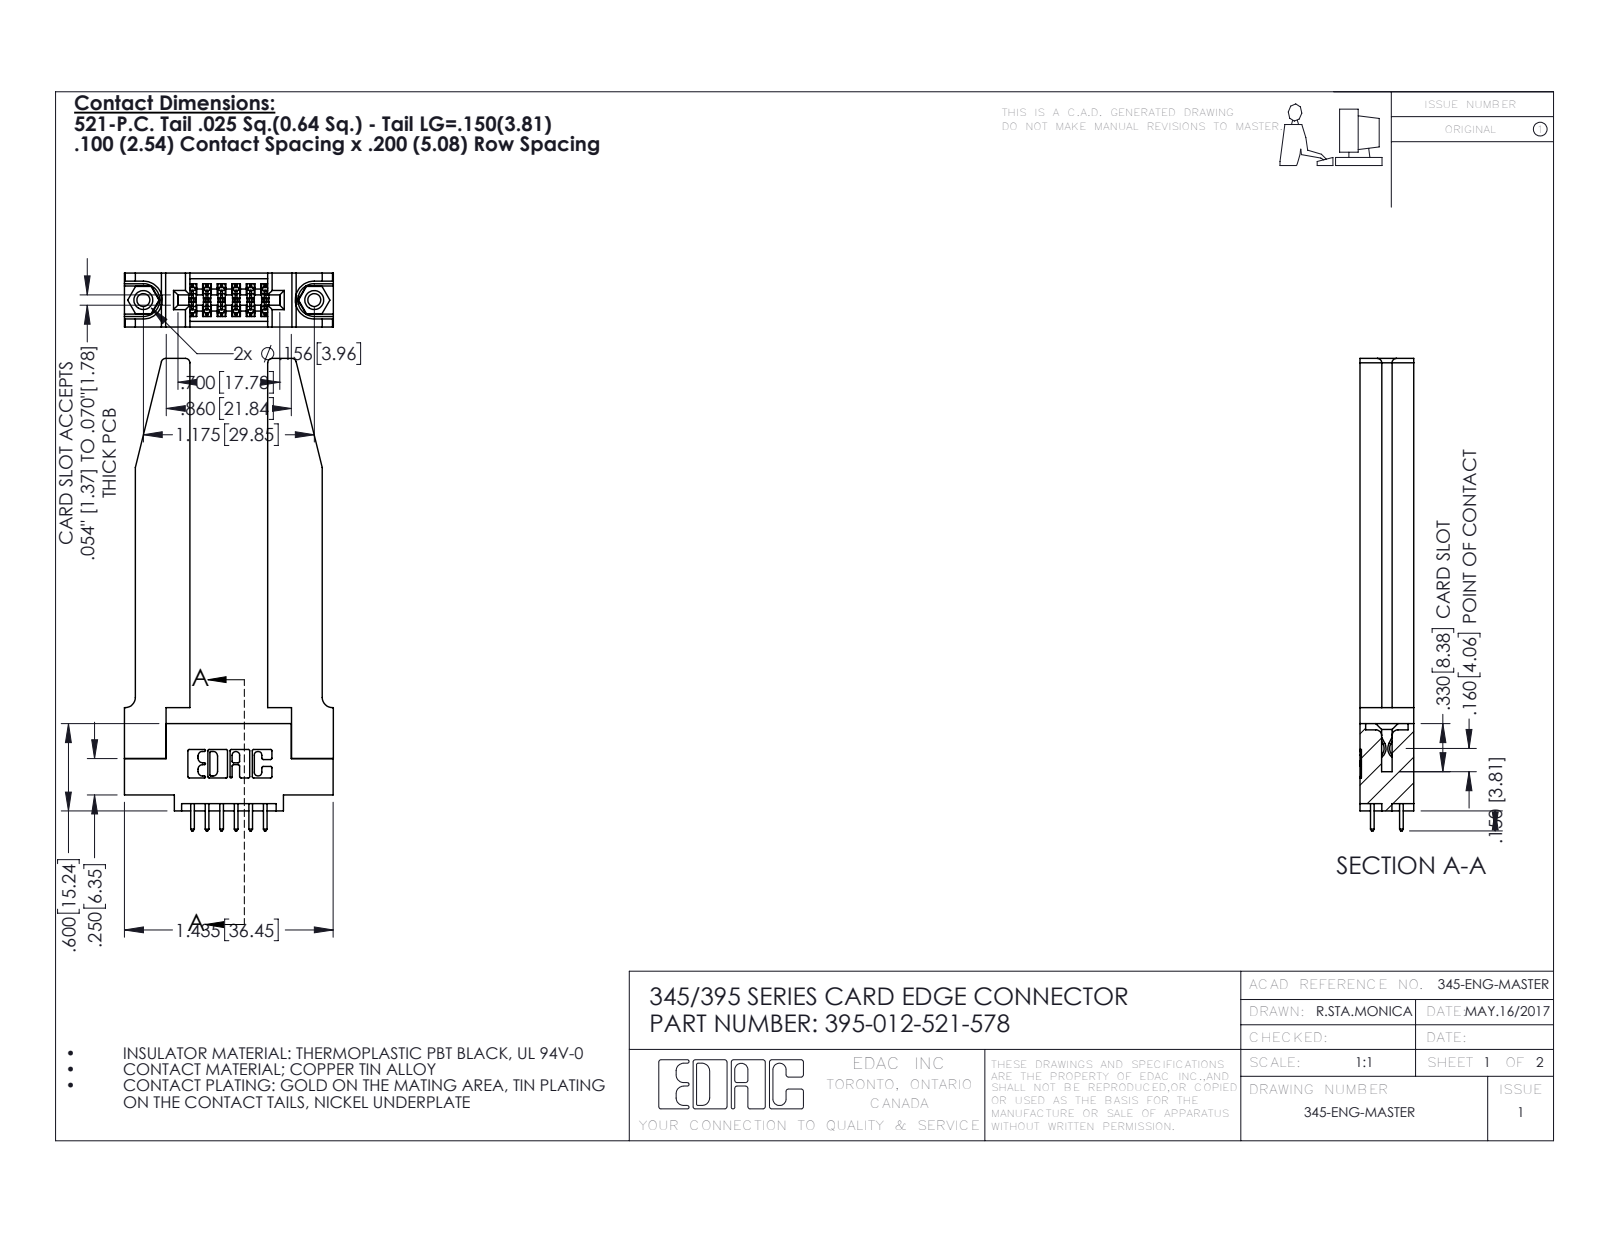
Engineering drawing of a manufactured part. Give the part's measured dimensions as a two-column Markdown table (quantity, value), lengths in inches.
| quantity | value |
| --- | --- |
| part name | 345-250-001_345-250-001-102; 345-220-078_345-220-078; 345-292-001_345-293-121; 345 Part_0.110 Offset - 0.156 Dia-TH (+1 more) |
| STEP written by | SolidWorks 2016 (CONFIG_CONTROL_DESIGN) |
| units | inches |
| bodies | 17 solids, 964 faces (622 planar, 290 cylindrical, 52 other) |
| overall size | 3.247 × 1.436 × 0.37 |
| volume | 0.665 in³ |
| surface area | 16.79 in² |
| round holes (diameter × count) | 0.089 × 2, 0.125 × 2, 0.156 × 2, 0.064 × 1 |
| round bosses / shafts (diameter × count) | 0.155 × 2 |
| partial cylindrical surfaces (radius × count) | 0.01 × 22, 0.006 × 18, 0.01 × 12, 0.03 × 8, 0.007 × 6, 0.031 × 6, 0.026 × 3, 0.014 × 2 |
| main face-to-face distances | 0.37, 0.15, 0.22, 0.072, 0.148, 0.535, 0.298, 0.077, 0.2, 0.071 |
| hole center spacings | 0.27, 0.946, 1.175 |
